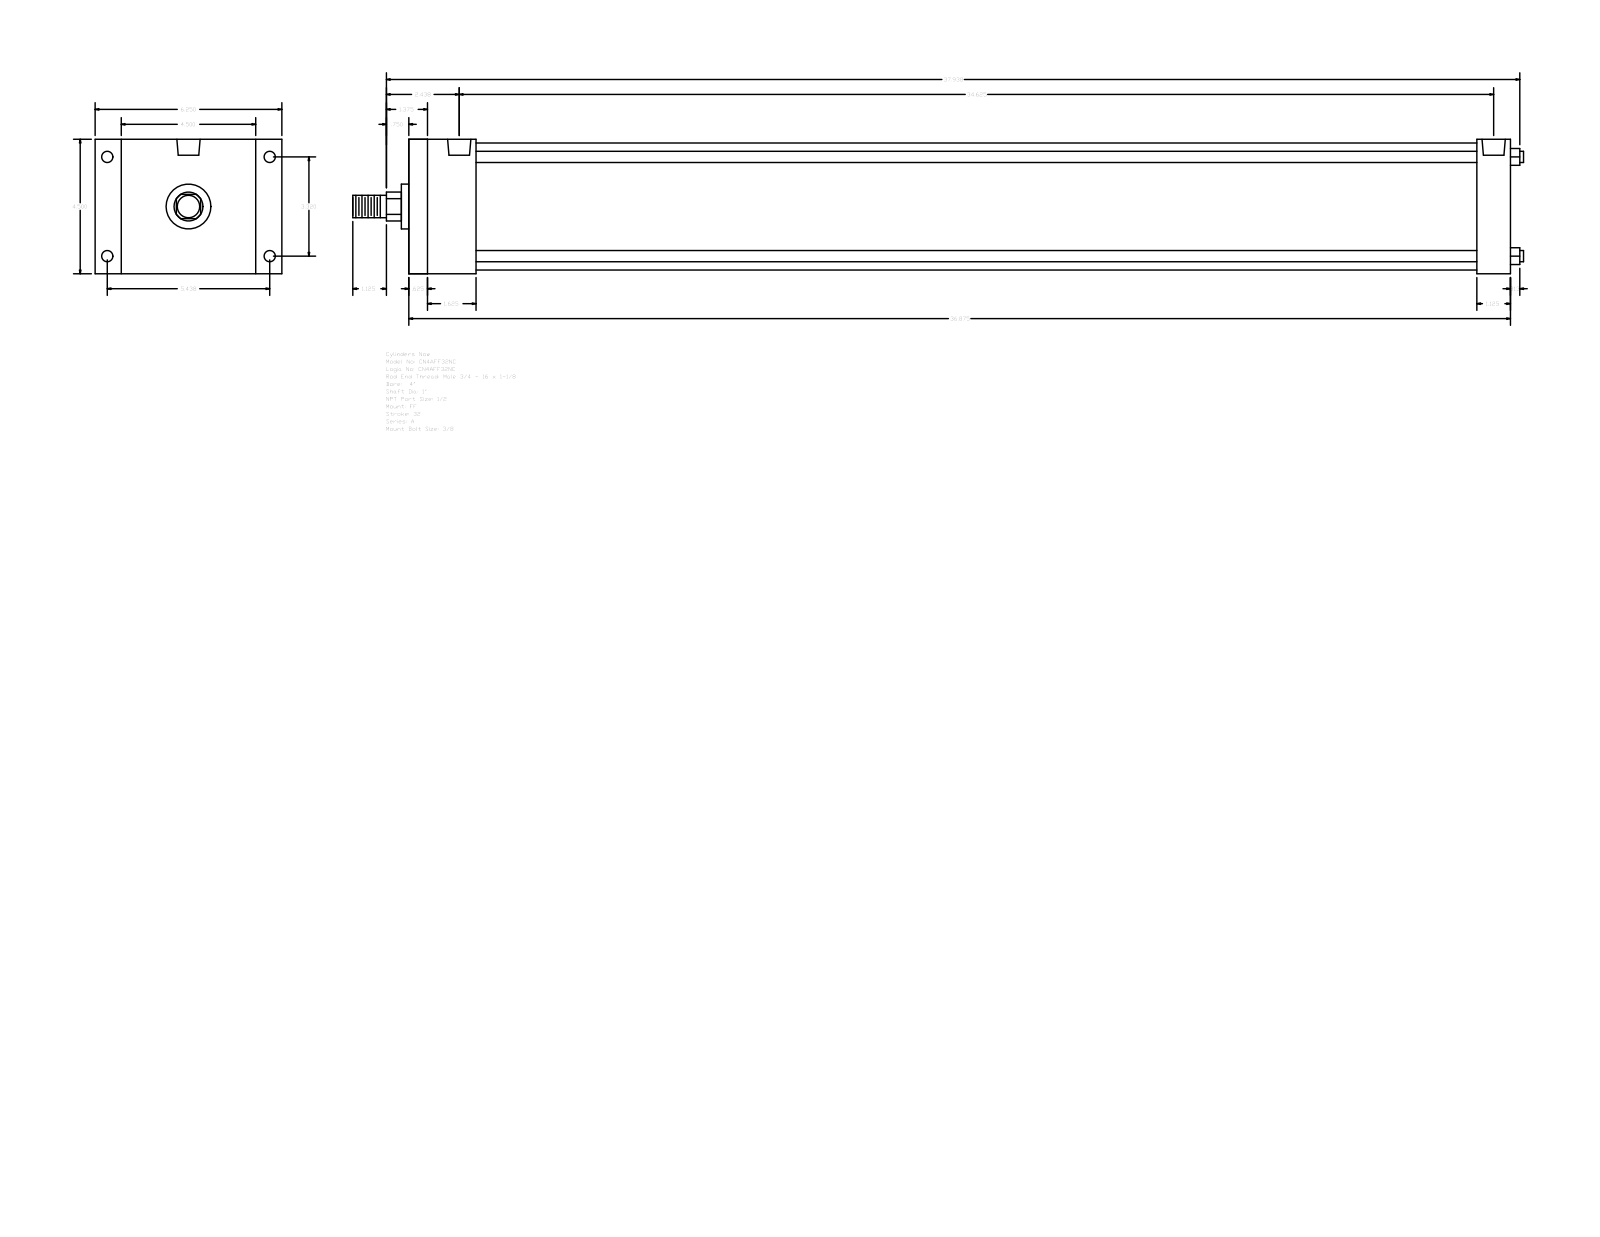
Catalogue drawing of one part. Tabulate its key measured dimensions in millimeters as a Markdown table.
| quantity | value |
| --- | --- |
| part name | A_FF__0400_1 |
| STEP written by | GSSL Pune (CONFIG_CONTROL_DESIGN) |
| units | millimeters |
| bodies | 0 solids, 92 faces (64 planar, 28 cylindrical, 0 other) |
| overall size | 995.36 × 158.75 × 114.3 |
| round holes (diameter × count) | 8.73 × 4, 9.53 × 4, 19.77 × 2 |
| round bosses / shafts (diameter × count) | 9.53 × 4, 107.95 × 1, 38.1 × 1, 25.4 × 1, 19.05 × 1 |
| partial cylindrical surfaces (radius × count) | 12.29 × 1 |
| main face-to-face distances | 114.3, 936.62, 15.87, 920.75, 28.57, 22.23, 136.53, 908.05, 892.18, 57.15 |
| hole center spacings | 3.18, 84.32, 138.12, 161.82, 873.12, 876.3, 879.48 |
